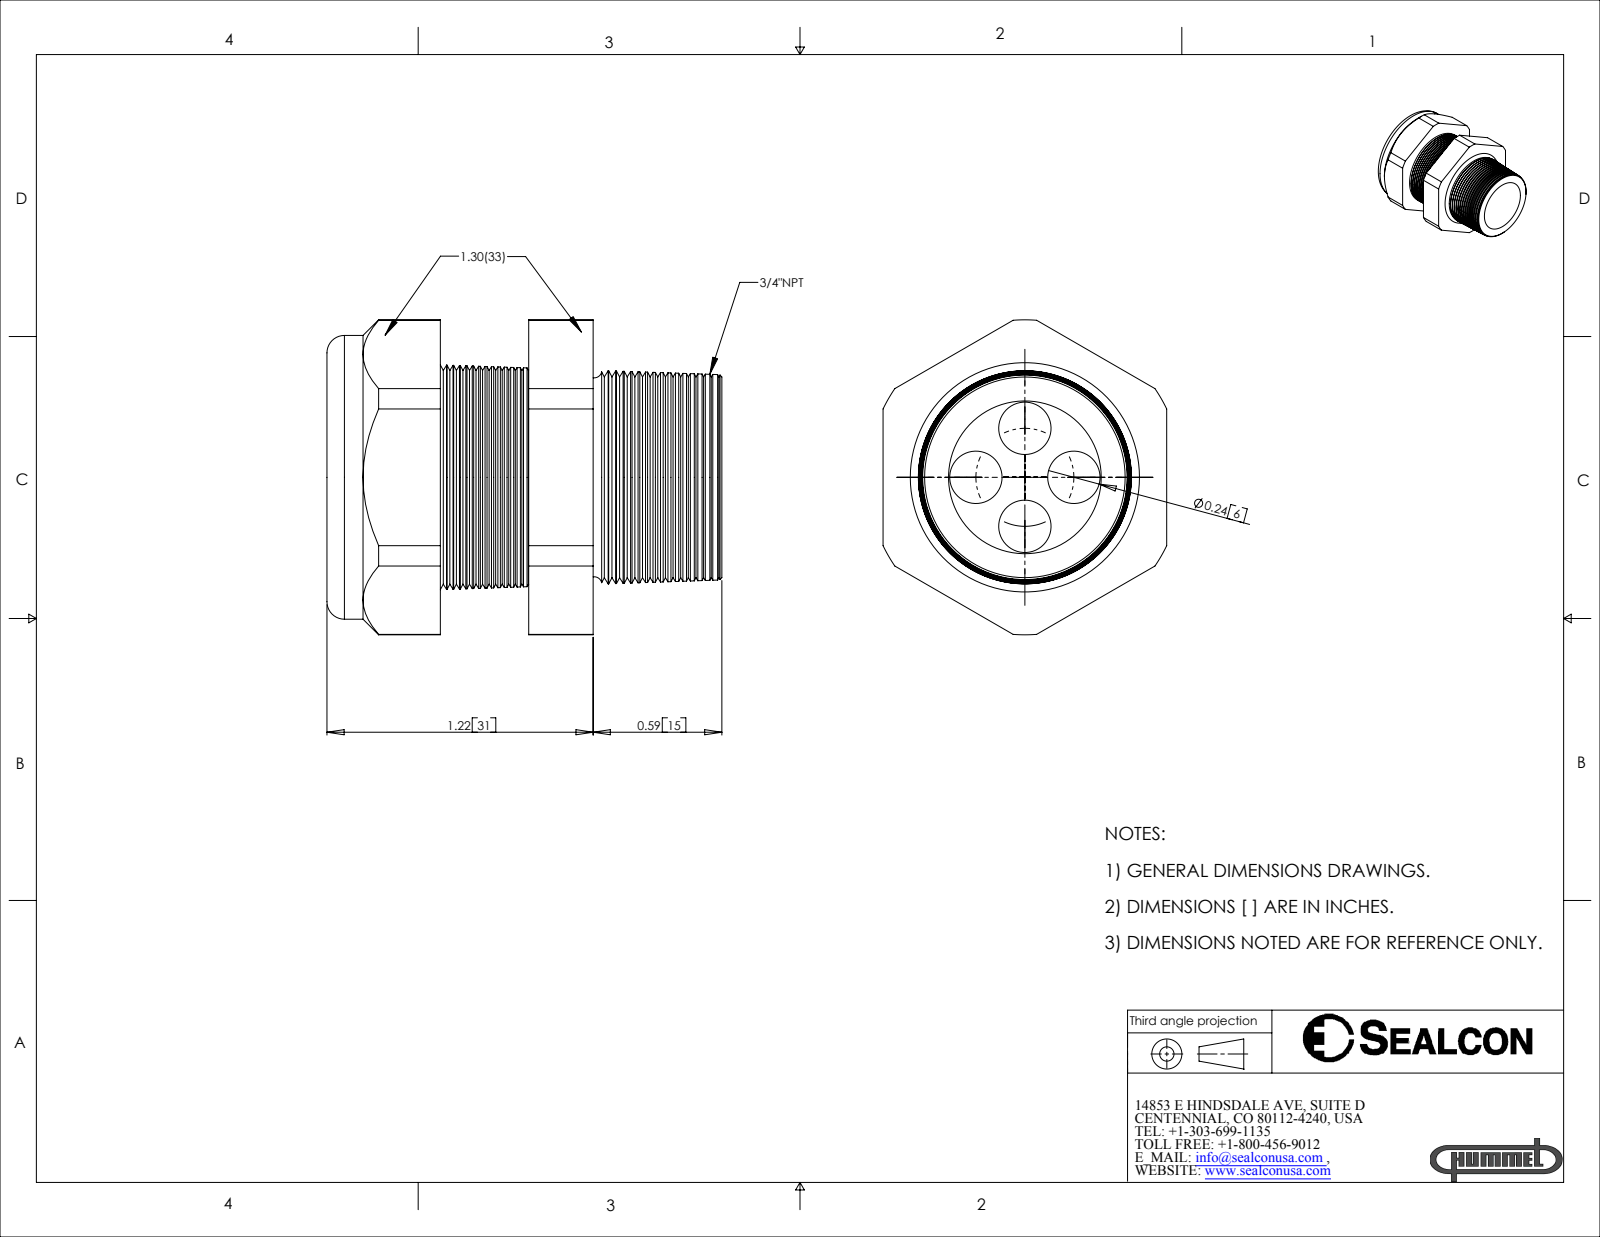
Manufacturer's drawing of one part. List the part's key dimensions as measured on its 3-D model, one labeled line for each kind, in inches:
Part name (STEP PRODUCT): CD21N1-GY
STEP written by: SolidWorks 2007 (CONFIG_CONTROL_DESIGN)
Units: inches
Bodies: 2 solids, 236 faces (20 planar, 28 cylindrical, 188 other)
Overall size (bounding box): 1.77 × 1.443 × 1.3
Volume: 1.23 in³ · Surface area: 17.97 in²
Round holes (diameter × count): ⌀0.24 ×4, ⌀0.69 ×1, ⌀0.71 ×1
Round bosses / shafts (diameter × count): ⌀1.3 ×1
Partial cylindrical surfaces — rounded edges, fillets, slot ends (radius × count): R0.721 ×1
Main face-to-face distances: 1.3, 0.925, 0.52, 0.405, 1.22, 0.7, 0.295, 1.77, 1.25, 0.845
Hole centre spacings: 0.224, 0.317, 0.449
